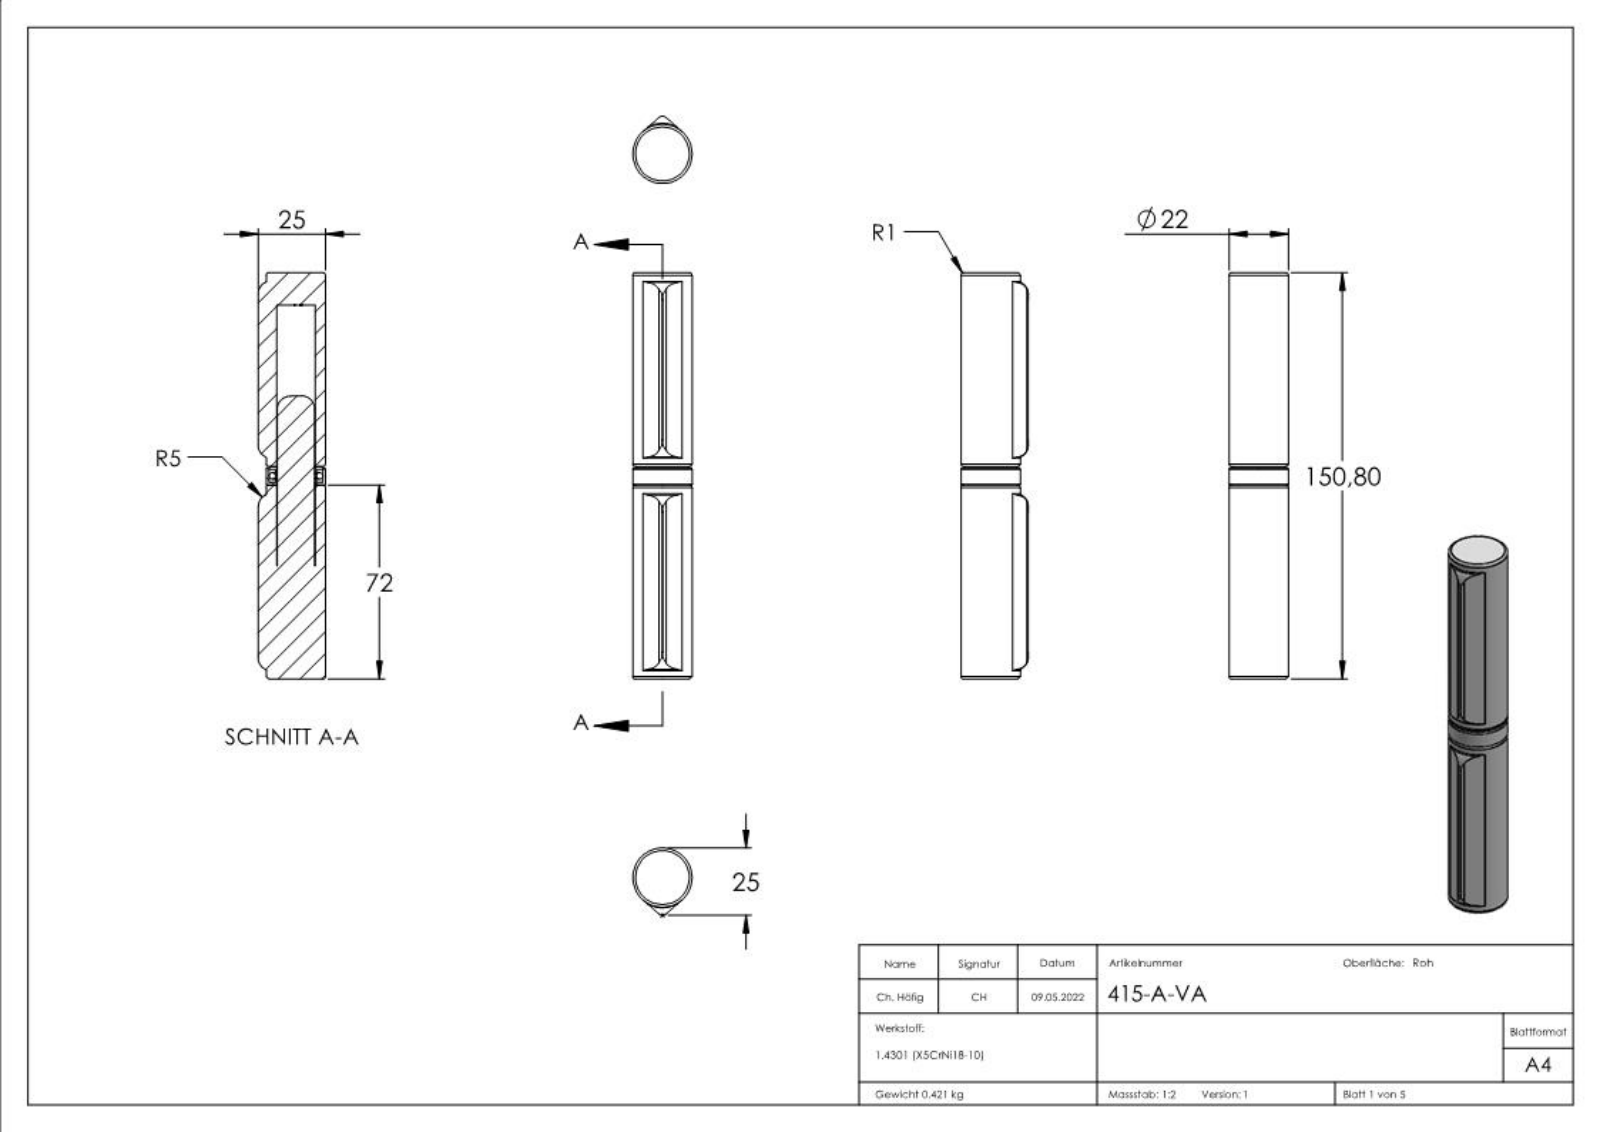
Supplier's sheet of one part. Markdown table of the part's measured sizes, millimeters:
| quantity | value |
| --- | --- |
| part name | 415-A-VA; 415-A-VA Teil2_415-A-VA Teil2; 415-A-VA Teil1_415-A-VA Teil1; 415-A-VA Teil3_415-A-VA Teil3 |
| STEP written by | SolidWorks 2018 (CONFIG_CONTROL_DESIGN) |
| units | millimeters |
| bodies | 23 solids, 284 faces (166 planar, 19 cylindrical, 99 other) |
| overall size | 150.8 × 25 × 22 |
| volume | 53 301 mm³ |
| surface area | 20 622 mm² |
| round holes (diameter × count) | 14.1 × 1, 14.2 × 1, 20 × 1 |
| round bosses / shafts (diameter × count) | 22 × 1, 15.2 × 1, 14 × 1 |
| partial cylindrical surfaces (radius × count) | 2 × 2, 14 × 1 |
| main face-to-face distances | 78.8, 72, 150.8, 1, 73, 77.8, 5.8, 6.8, 138.8, 66.8 |
